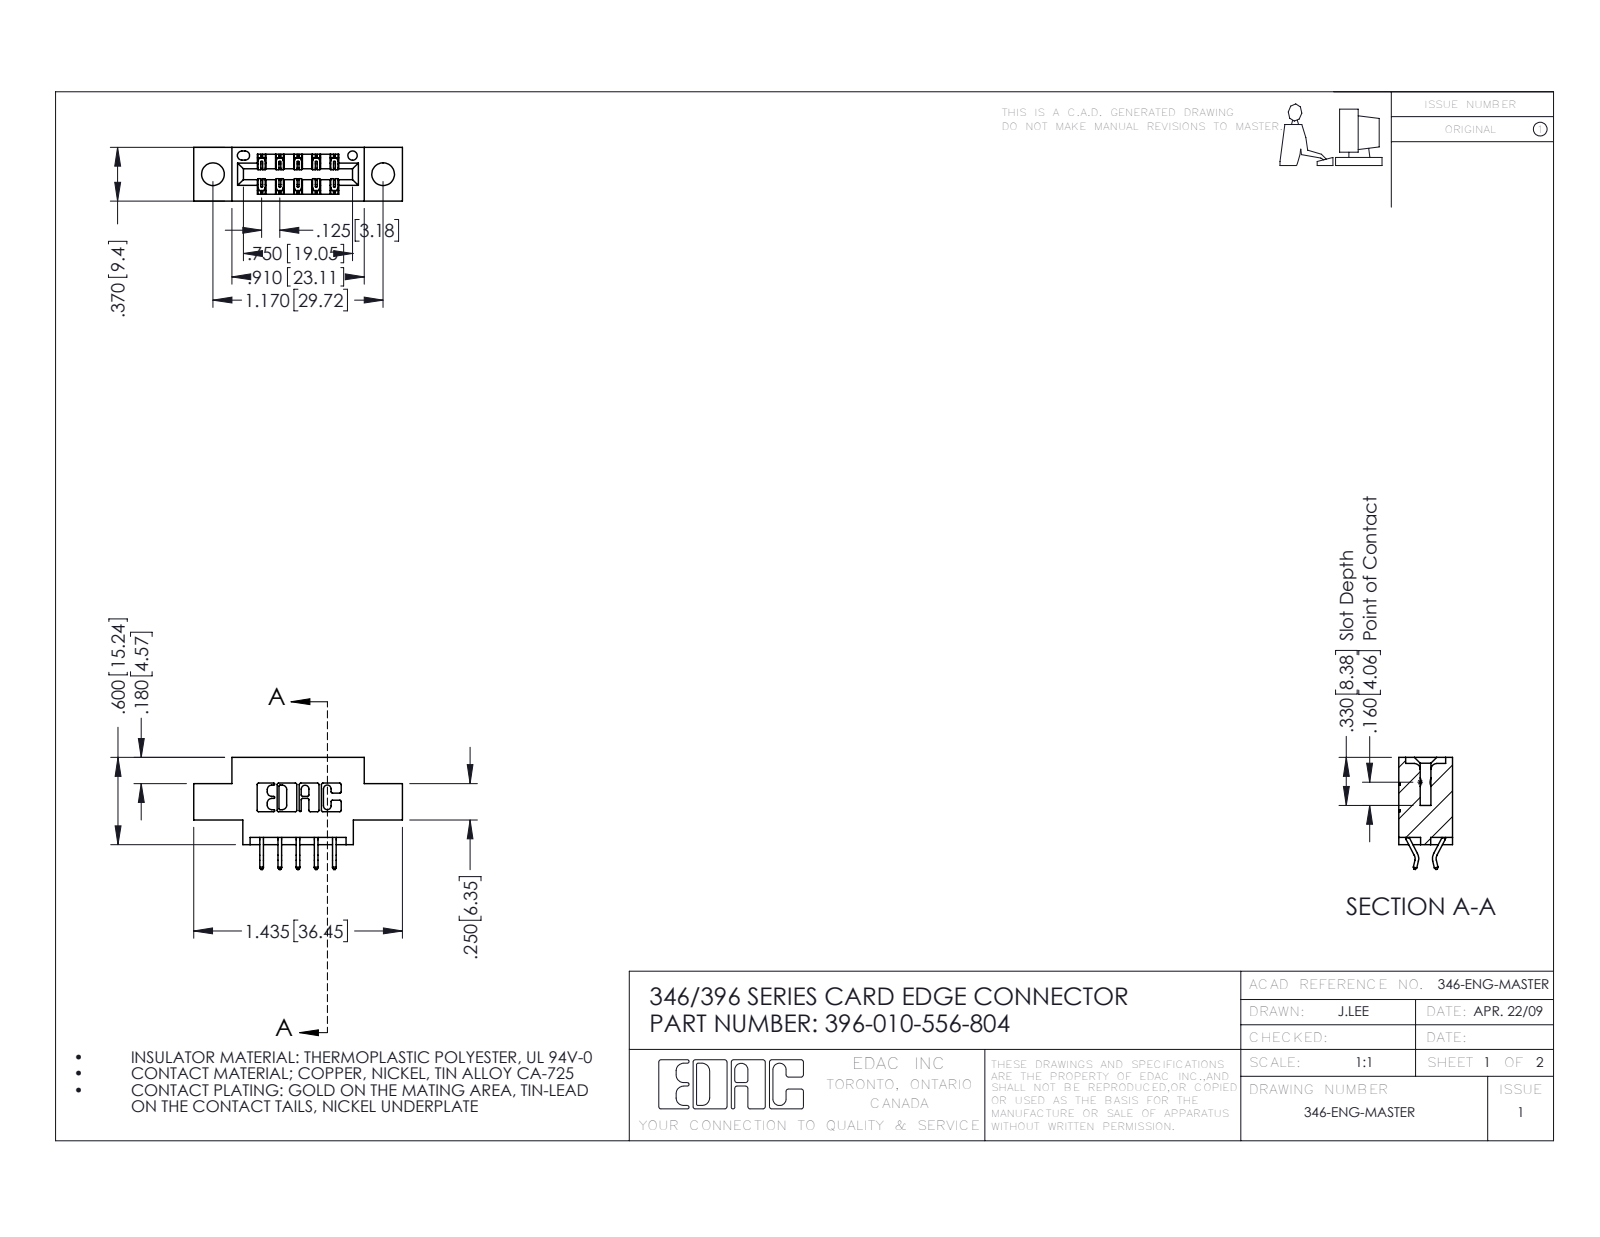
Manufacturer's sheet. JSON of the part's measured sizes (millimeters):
{"part_name": "346 Part_0.170 Offset - 0.156 Dia-TH; 396-010-556-804; 345-292-001_556 Tail", "step_written_by": "SolidWorks 2016 (CONFIG_CONTROL_DESIGN)", "units": "millimeters", "bodies": {"solids": 11, "faces": 706, "planar": 470, "cylindrical": 236, "other": 0}, "overall_size": [36.4, 19.6, 9.4], "volume_mm3": 3030, "surface_area_mm2": 3559, "round_holes": [[4, 2], [1.6, 1]], "partial_cylinders_radius": [[0.3, 22], [0.2, 15], [0.2, 6], [0.8, 6], [0.7, 3], [0.3, 2], [0.4, 2], [0.6, 2]], "face_to_face_distances": [6.4, 9.4, 1.2, 8.2, 3.8, 5.6, 2.5, 4.4, 0.6, 1.8], "hole_center_spacings": [6.2, 24.6, 29.7]}
